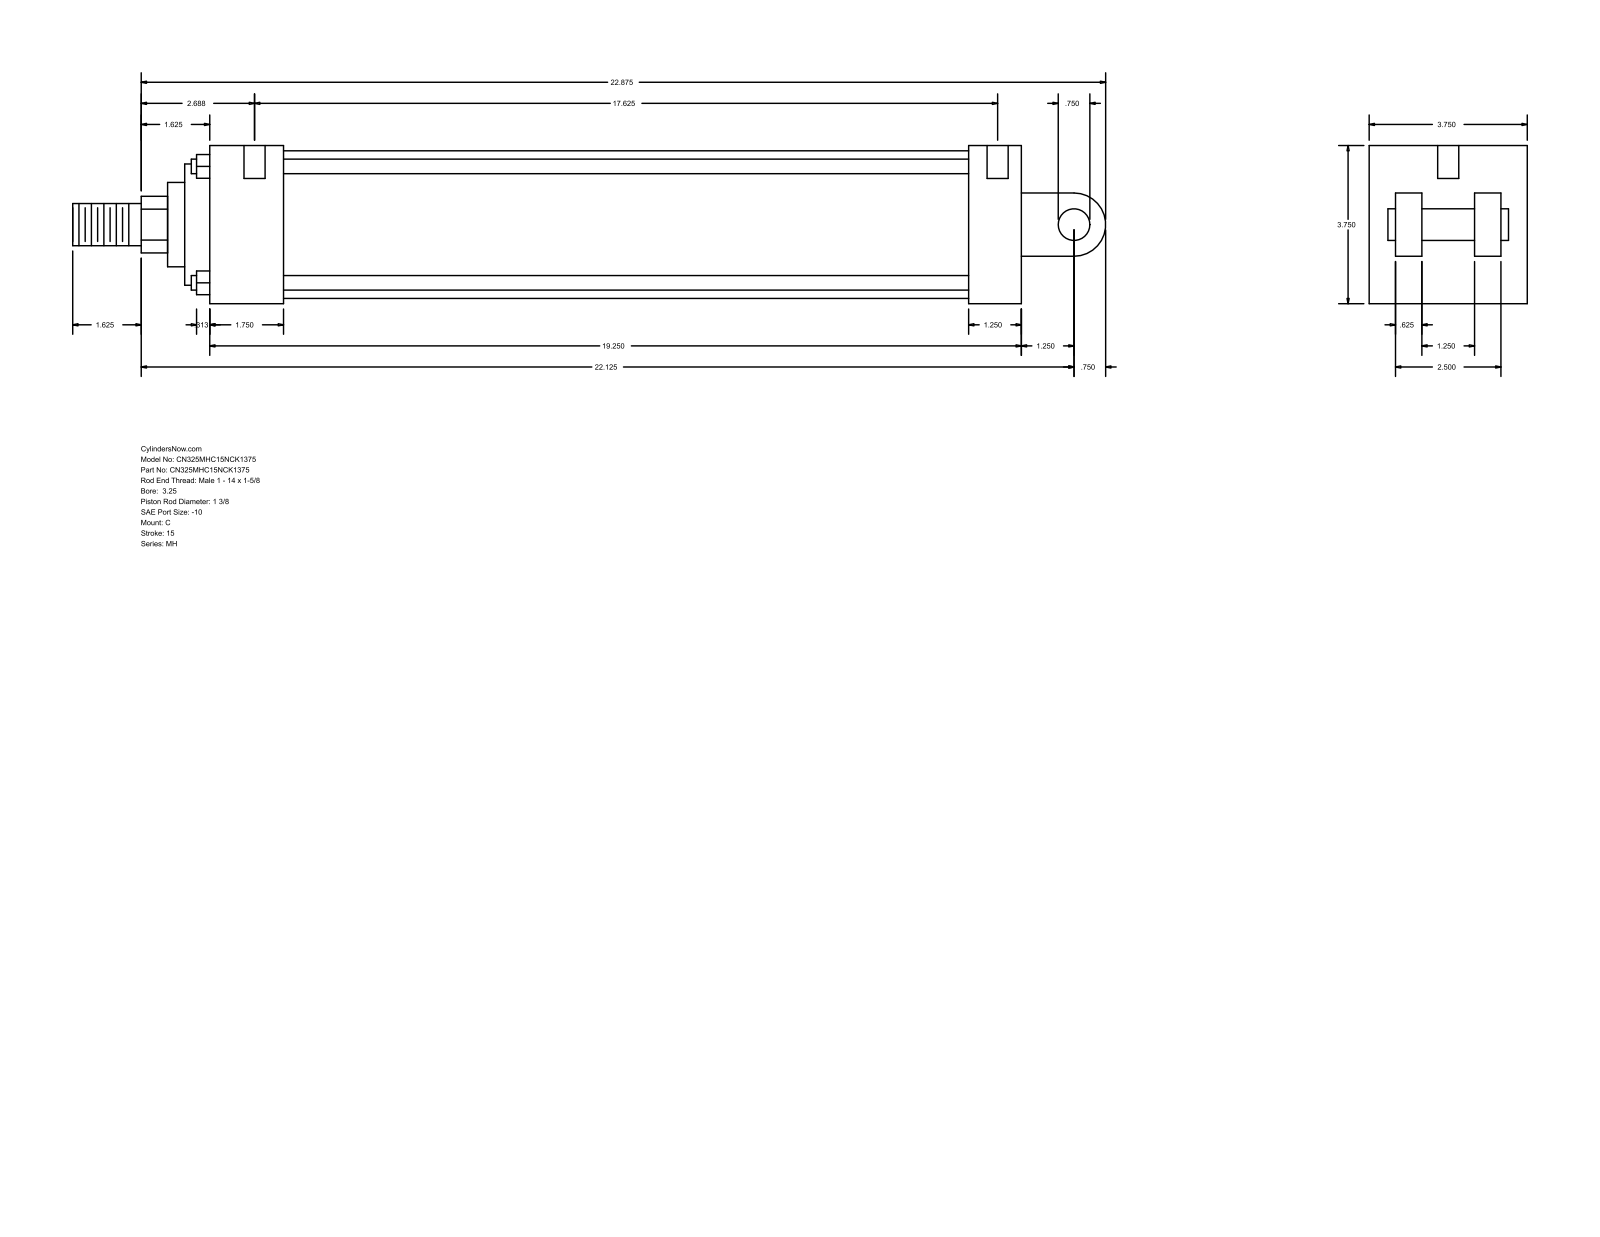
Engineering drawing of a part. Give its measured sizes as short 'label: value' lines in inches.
name: MH_C__0325_1.375
written by: GSSL Pune (CONFIG_CONTROL_DESIGN)
unit: in
bodies: 0 solids, 101 faces (71 planar, 30 cylindrical, 0 other)
size: 24.5 × 3.75 × 3.75
holes: 4× ⌀0.219, 2× ⌀0.5
bosses: 4× ⌀0.345, 1× ⌀3.5, 1× ⌀2.875, 1× ⌀2, 1× ⌀1.375, 1× ⌀1, 1× ⌀0.75
rounds: 1× R0.672, 1× R0.75
face distances: 3.75, 0.625, 2.5, 19.25, 1.25, 3.125, 1.875, 1.75, 18, 16.25
hole spacings: 17.875, 0.063, 0.187, 17.625, 17.688, 17.813
